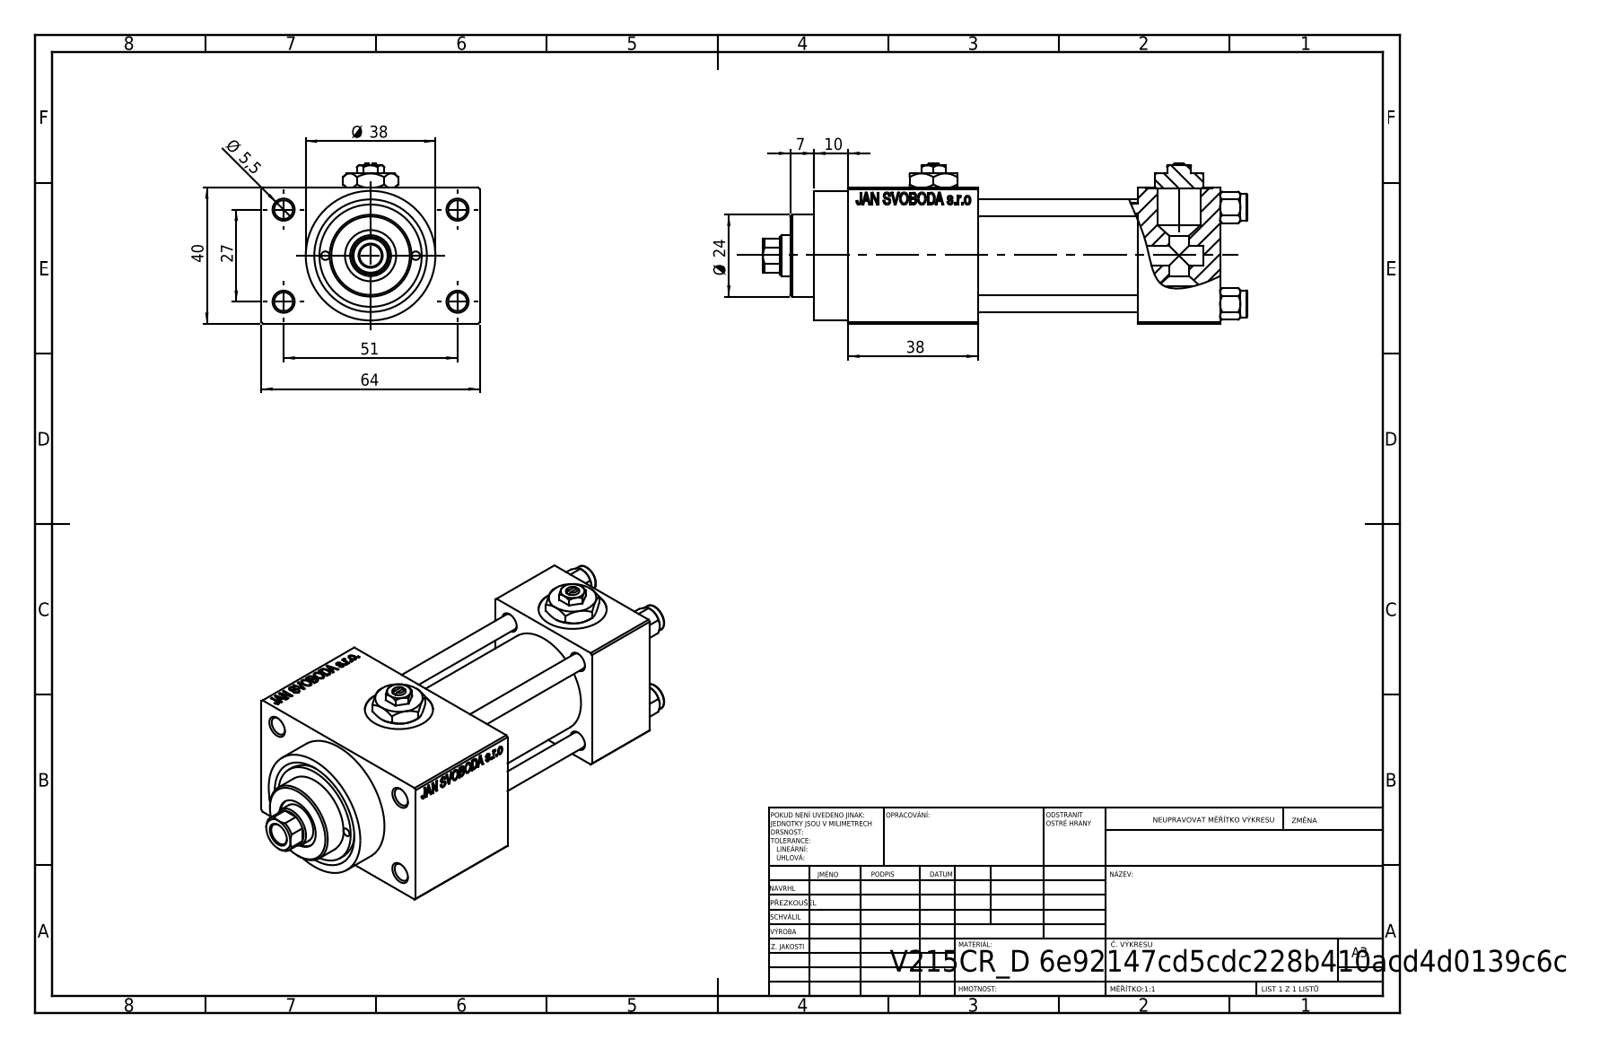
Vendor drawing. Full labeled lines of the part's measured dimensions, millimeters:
Part name (STEP PRODUCT): NUT_M5_D; V215CR_D_Body; V215CR_D_TYCINKA; V215CR_VCP_D (+2 more)
STEP written by: SolidWorks 2019 (CONFIG_CONTROL_DESIGN)
Units: millimetres
Bodies: 13 solids, 1210 faces (544 planar, 104 cylindrical, 562 other)
Overall size (bounding box): 142 × 64 × 47
Volume: 174 055 mm³ · Surface area: 63 313 mm²
Round holes (diameter × count): ⌀5 ×4, ⌀5.5 ×4, ⌀20 ×3, ⌀2.5 ×2, ⌀7 ×2, ⌀13.16 ×2, ⌀6.5 ×1, ⌀12 ×1, ⌀15 ×1, ⌀25 ×1, ⌀30 ×1
Round bosses / shafts (diameter × count): ⌀8 ×4, ⌀38 ×1, ⌀31 ×1, ⌀24 ×1
Partial cylindrical surfaces — rounded edges, fillets, slot ends (radius × count): R5.5 ×1
Main face-to-face distances: 40, 52, 12, 47, 24, 71, 64, 38, 85, 109
Hole centre spacings: 11.37, 14.18, 18.23, 20.01, 28.3, 28.85, 29.89, 30.84
